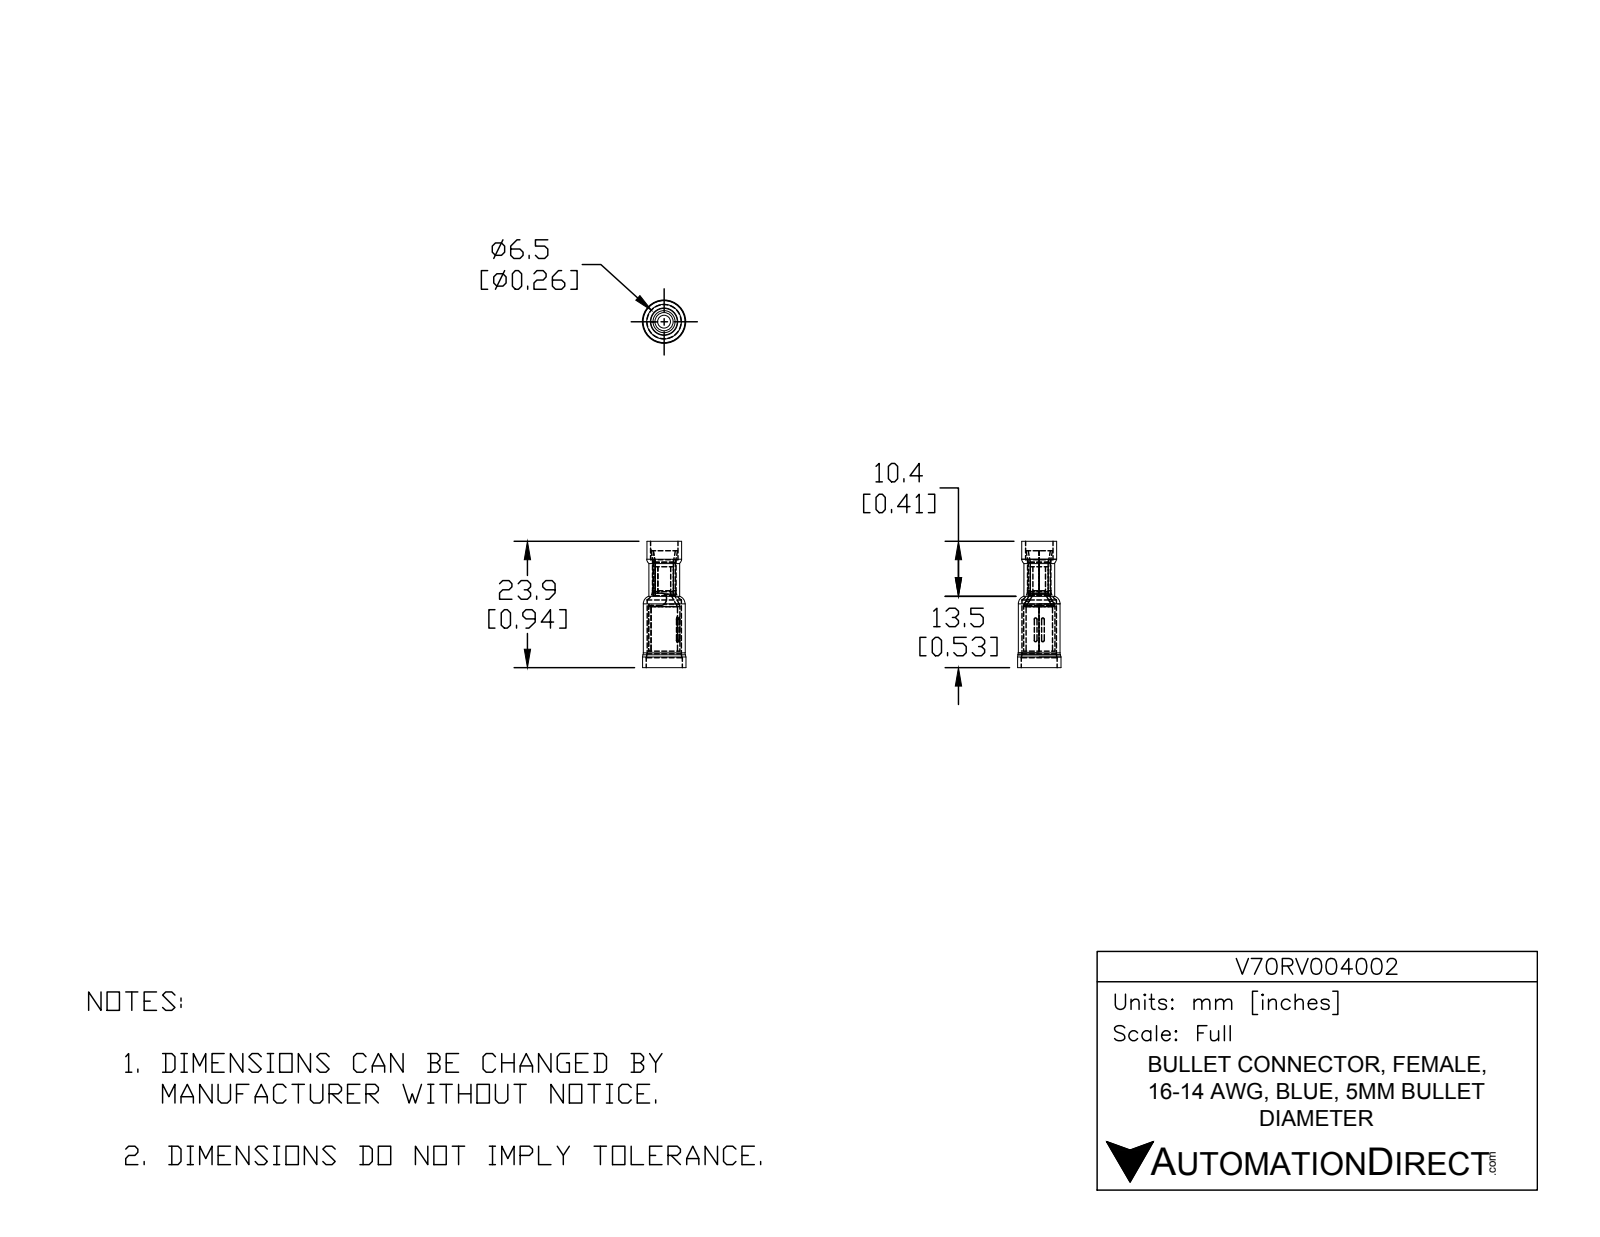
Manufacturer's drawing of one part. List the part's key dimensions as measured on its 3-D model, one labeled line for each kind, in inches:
Part name (STEP PRODUCT): V70RV004002
STEP written by: SolidWorks 2017 (AUTOMOTIVE_DESIGN)
Units: inches
Bodies: 3 solids, 89 faces (23 planar, 40 cylindrical, 26 other)
Overall size (bounding box): 0.941 × 0.323 × 0.323
Volume: 0.029 in³ · Surface area: 2.633 in²
Round holes (diameter × count): ⌀0.094 ×1, ⌀0.174 ×1, ⌀0.197 ×1, ⌀0.205 ×1, ⌀0.256 ×1, ⌀0.268 ×1
Round bosses / shafts (diameter × count): ⌀0.323 ×1, ⌀0.311 ×1, ⌀0.26 ×1, ⌀0.232 ×1, ⌀0.229 ×1, ⌀0.165 ×1, ⌀0.134 ×1
Partial cylindrical surfaces — rounded edges, fillets, slot ends (radius × count): R0.01 ×4, R0.039 ×2
Main face-to-face distances: 0.941, 0.122, 0.819, 0.803, 0.681, 0.138, 0.87, 0.748, 0.067, 0.071
